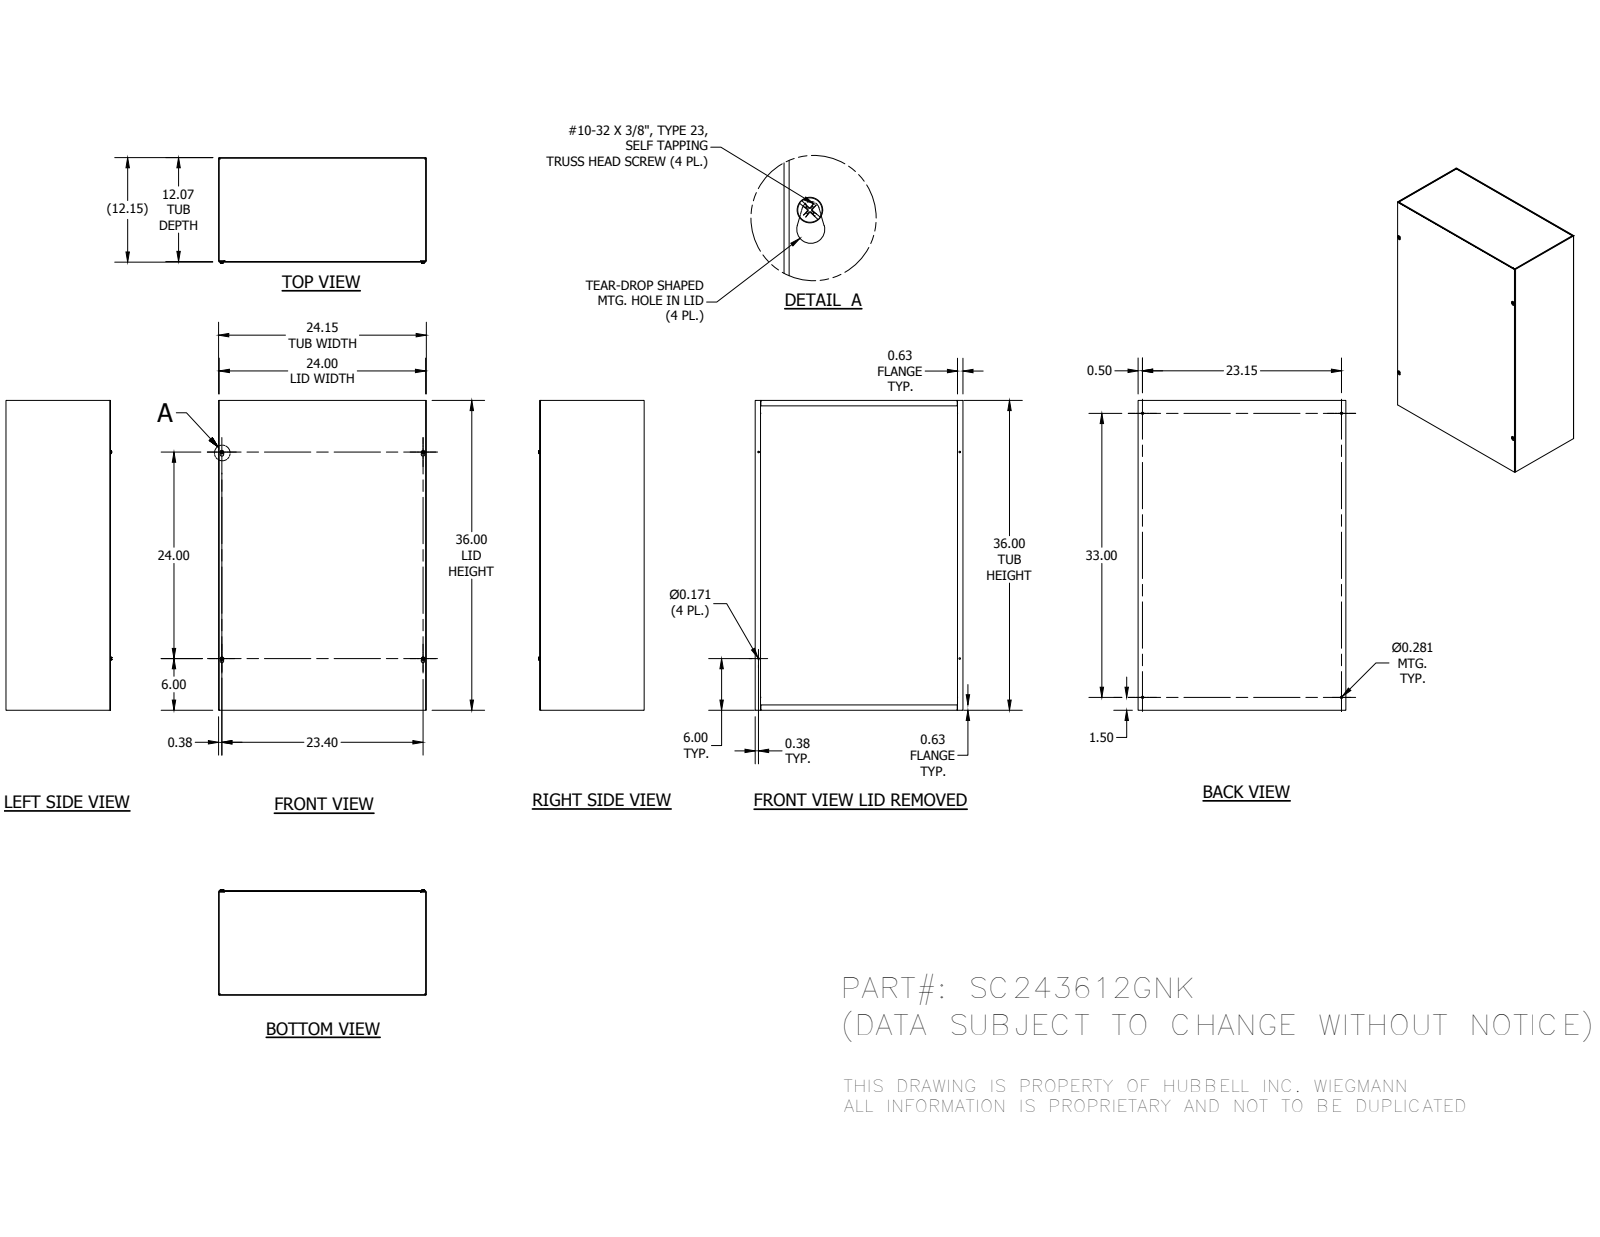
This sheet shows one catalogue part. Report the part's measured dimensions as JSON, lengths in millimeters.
{"part_name": "SC243612GNKBLR; SC2412GNKTB; SC2436GLPA; 37214 (+1 more)", "step_written_by": "Autodesk Inventor 2014 (AUTOMOTIVE_DESIGN)", "units": "millimeters", "bodies": {"solids": 8, "faces": 320, "planar": 192, "cylindrical": 44, "other": 84}, "overall_size": [914.4, 613.36, 311.91], "volume_mm3": 3982000, "surface_area_mm2": 4259000, "round_holes": [[4.34, 4], [7.14, 4]], "round_bosses_or_shafts": [[4.83, 4]], "partial_cylinders_radius": [[0.4, 12], [2.28, 12], [3.17, 4], [5.16, 4]], "face_to_face_distances": [1.88, 306.68, 304.8, 308.56, 611.48, 912.52, 609.6, 613.36, 914.4, 910.64], "hole_center_spacings": [114.34, 602.08, 723.91, 934.59, 587.96, 594.3, 609.6, 838.2]}
